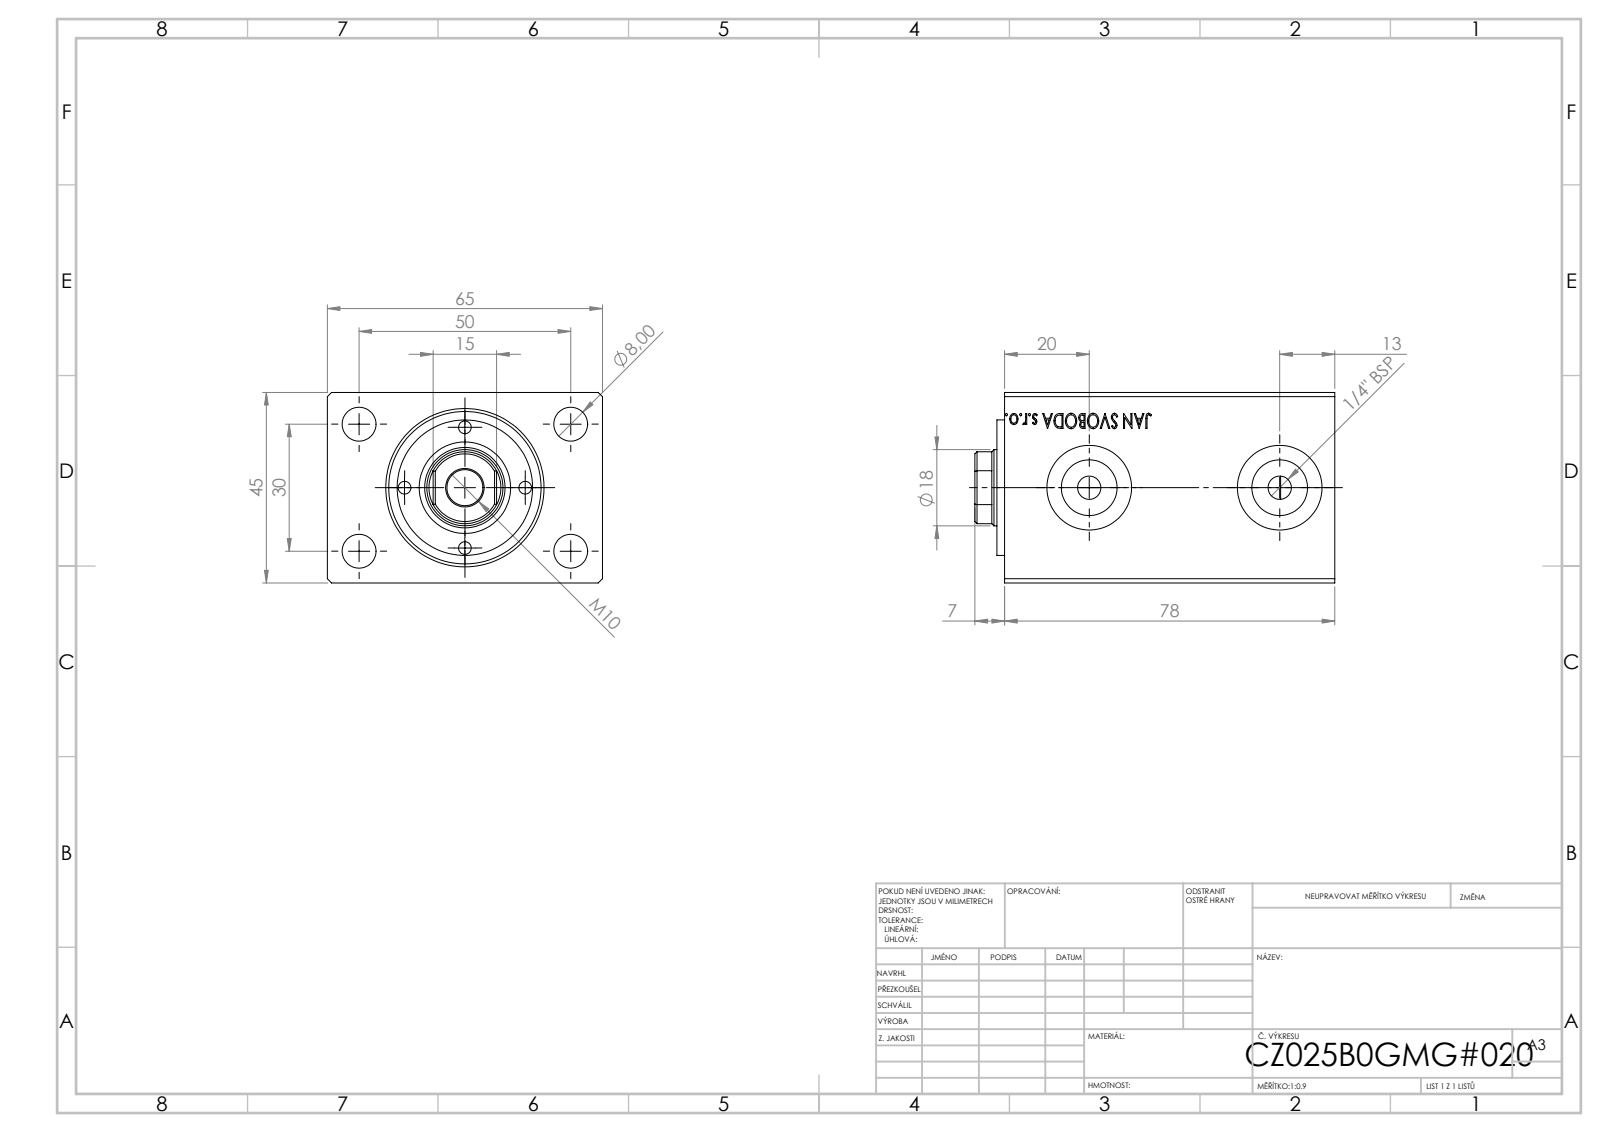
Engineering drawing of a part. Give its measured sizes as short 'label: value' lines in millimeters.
name: V500CZ; V500CZ_B_VC
written by: SolidWorks 2019 (CONFIG_CONTROL_DESIGN)
unit: mm
bodies: 3 solids, 873 faces (399 planar, 58 cylindrical, 416 other)
size: 85 × 65 × 45
volume: 209 110 mm³; area: 43 519 mm²
holes: 4× ⌀3, 4× ⌀8, 2× ⌀5.5, 2× ⌀13.16, 2× ⌀20, 1× ⌀8.5, 1× ⌀18, 1× ⌀19, 1× ⌀25, 1× ⌀36
bosses: 1× ⌀32
rounds: 1× R8.5
face distances: 45, 65, 78, 7, 77.8, 65.2, 12.6, 12.8, 1.8, 5.2
hole spacings: 14.25, 18.45, 20.15, 25.01, 29.15, 38.48, 42.02, 28.5
